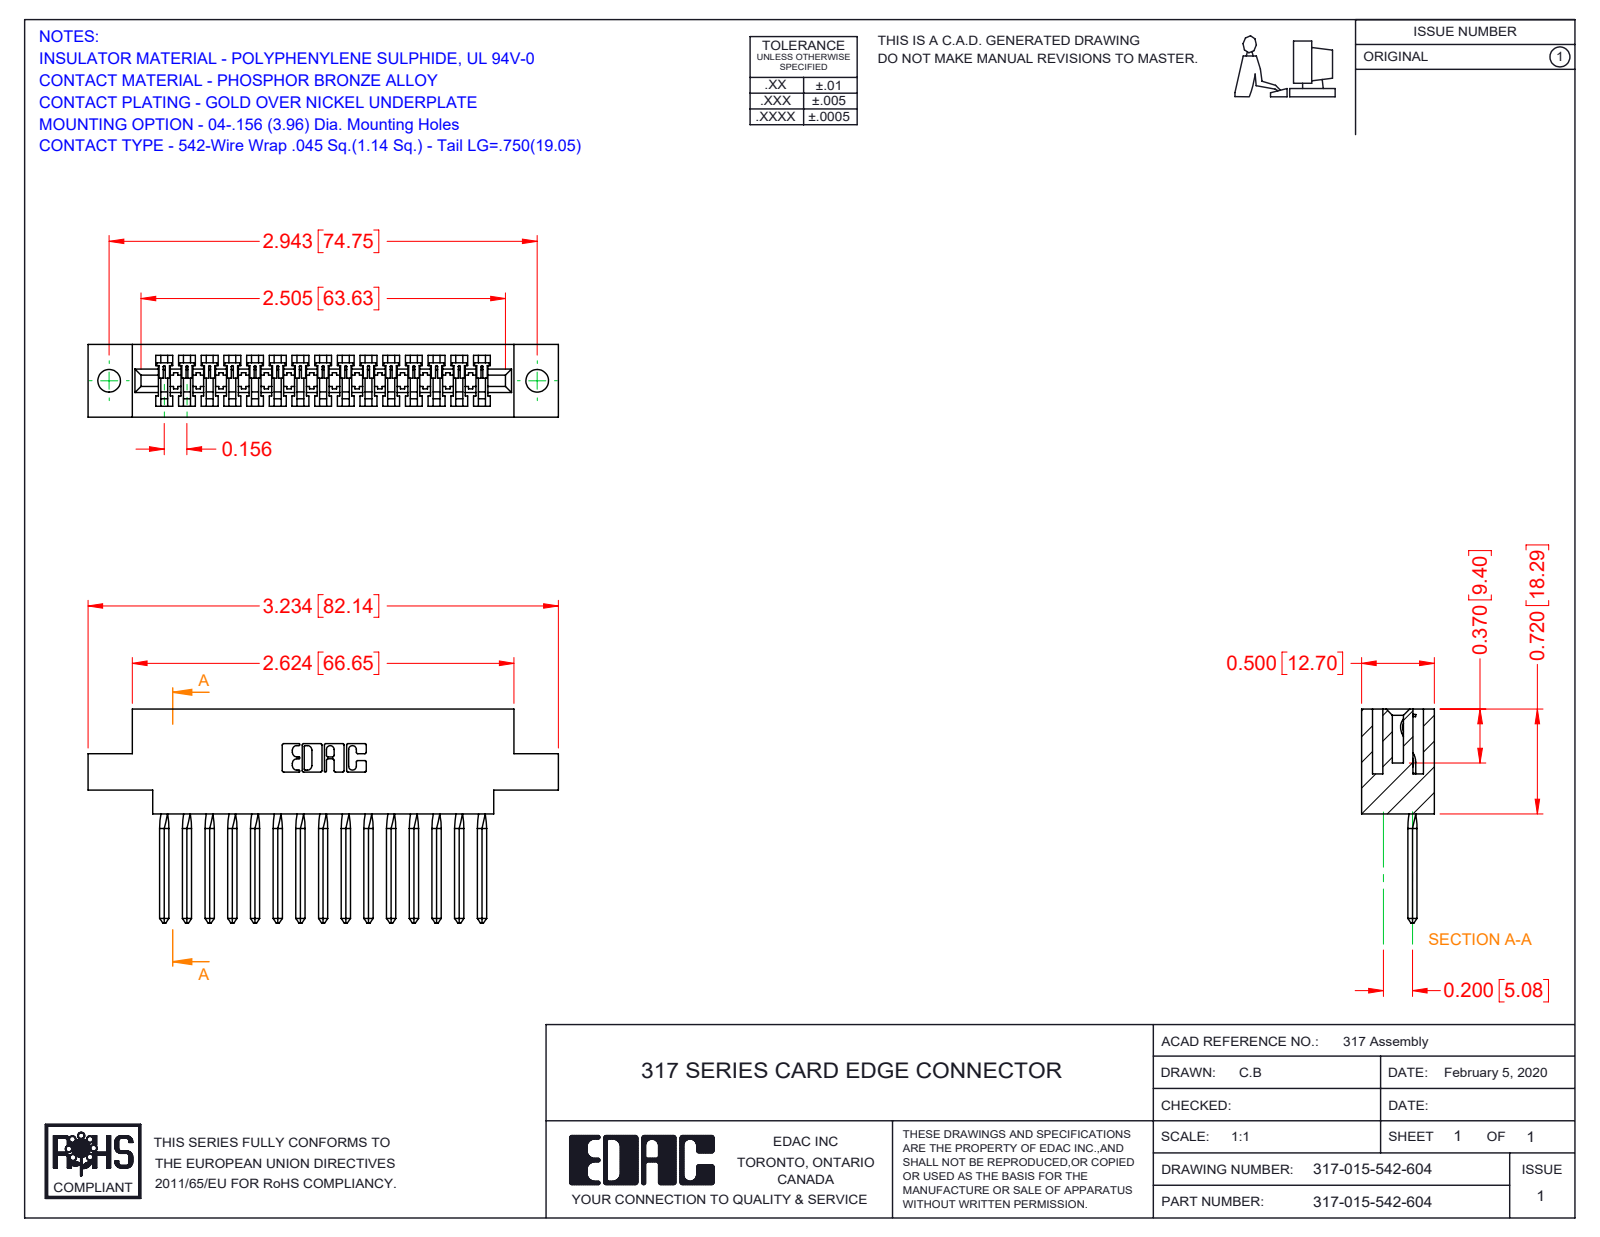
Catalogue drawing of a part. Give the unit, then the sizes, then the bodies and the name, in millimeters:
Units: millimetres
Overall size (bounding box): 82.1 × 37.3 × 12.7
Round holes (diameter × count): ⌀4 ×2
Partial cylindrical surfaces — rounded edges, fillets, slot ends (radius × count): R0.2 ×30, R0.3 ×22, R0.2 ×6, R0.8 ×6, R0.7 ×3, R1.9 ×1, R2.3 ×1, R2.5 ×1
Main face-to-face distances: 12.7, 1.9, 10.8, 2.8, 8.9, 1.7, 5.6, 3.5, 18.3, 7.1
Hole centre spacings: 74.8
Volume: 11 900 mm³ · Surface area: 13 700 mm²
Bodies: 16 solids, 1227 faces (1018 planar, 149 cylindrical, 60 other)
Part name (STEP PRODUCT): 317-015-542-604; 317 Part_.156 Dia - TH; 317-290-003_542
STEP written by: SolidWorks 2016 (CONFIG_CONTROL_DESIGN)
